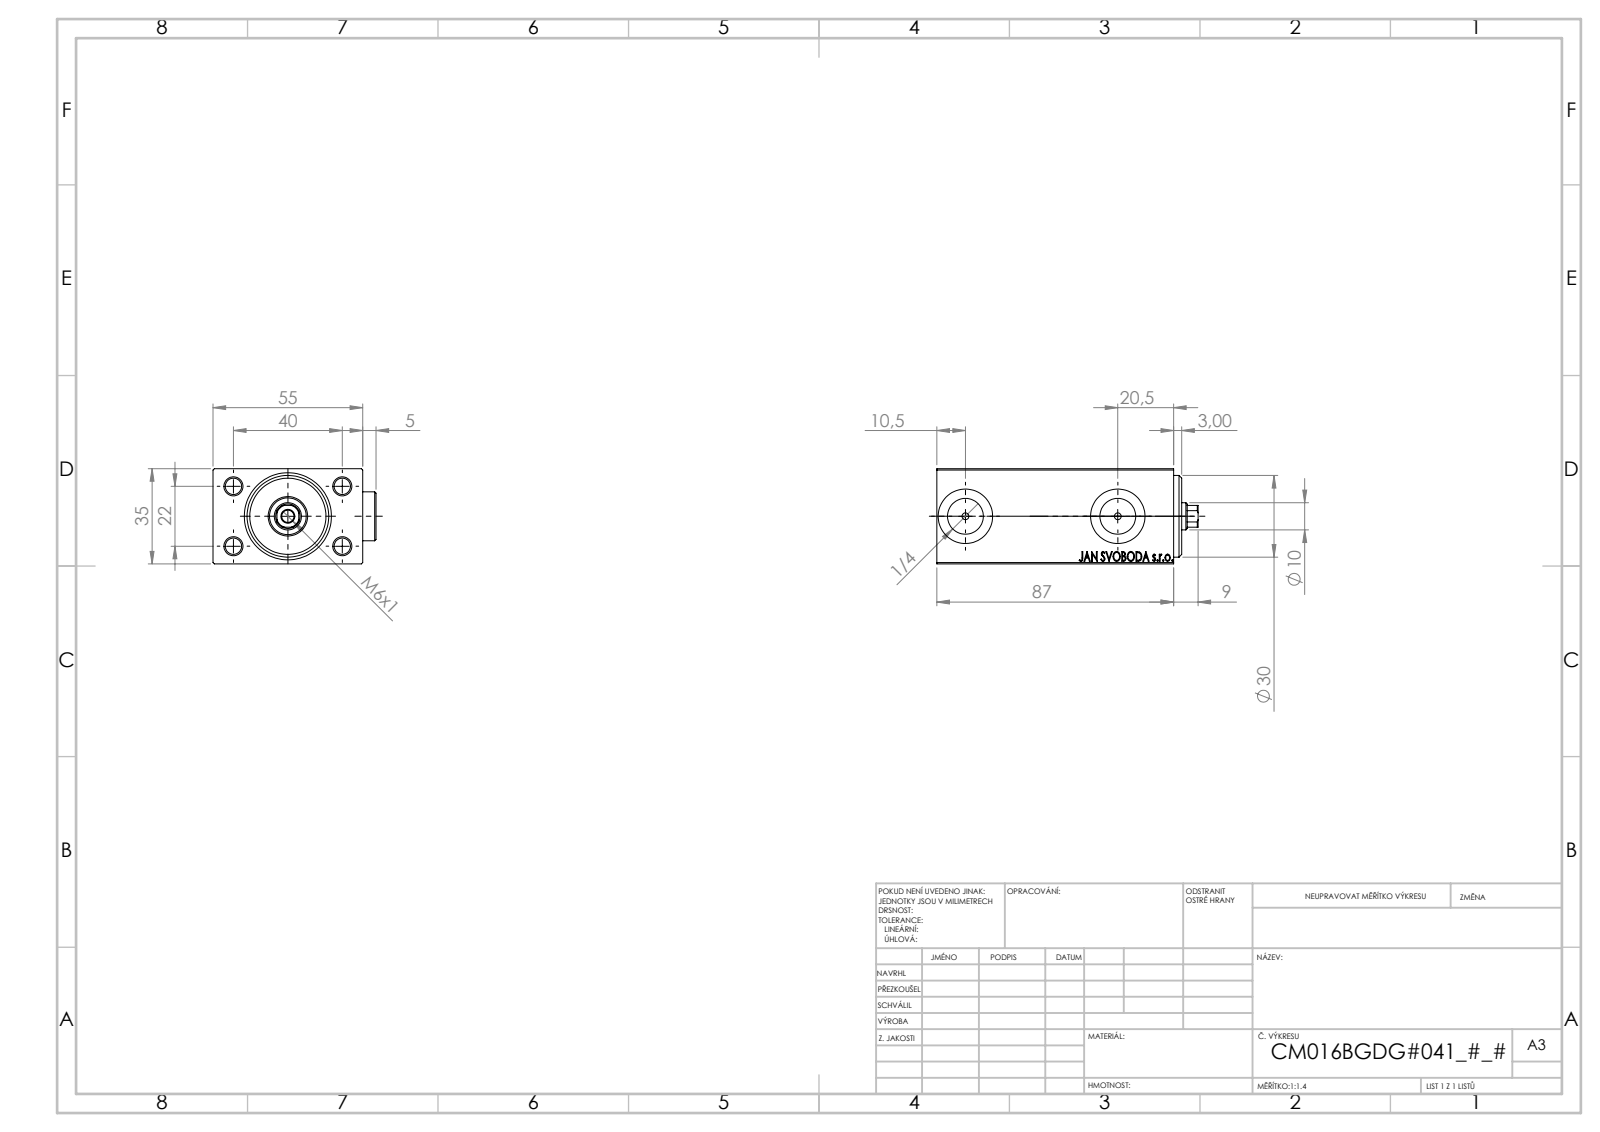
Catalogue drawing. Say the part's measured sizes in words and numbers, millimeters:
The part is named "V450CM_B_VCP; Zatka_OIL_PORT; V450CM_B_Body; V450CM_VC_B". Its 3-D file was written by "SolidWorks 2019 (CONFIG_CONTROL_DESIGN)". It is 5 solids with 935 faces: 435 planar, 70 cylindrical and 430 other. Overall it measures 96 by 59.9 by 35 millimeters. Its volume is 157 087 cubic millimeters and its surface area 35 948 square millimeters. Round holes: 4 of diameter 6, 2 of diameter 2.5, 2 of diameter 13.16, 2 of diameter 20, 1 of diameter 4.5, 1 of diameter 10, 1 of diameter 13.5, 1 of diameter 14.5, 1 of diameter 16, 1 of diameter 18, 1 of diameter 30. Round bosses or shafts: 2 of diameter 18. Partial cylindrical surfaces (rounded edges, fillets, slot ends): 1 of radius 4.5. The main face-to-face distances are 35, 55, 5, 82, 54.9, 87, 3, 8, 90, 54.8. The hole center spacings are 22.83, 22, 40, 45.65, 56.
